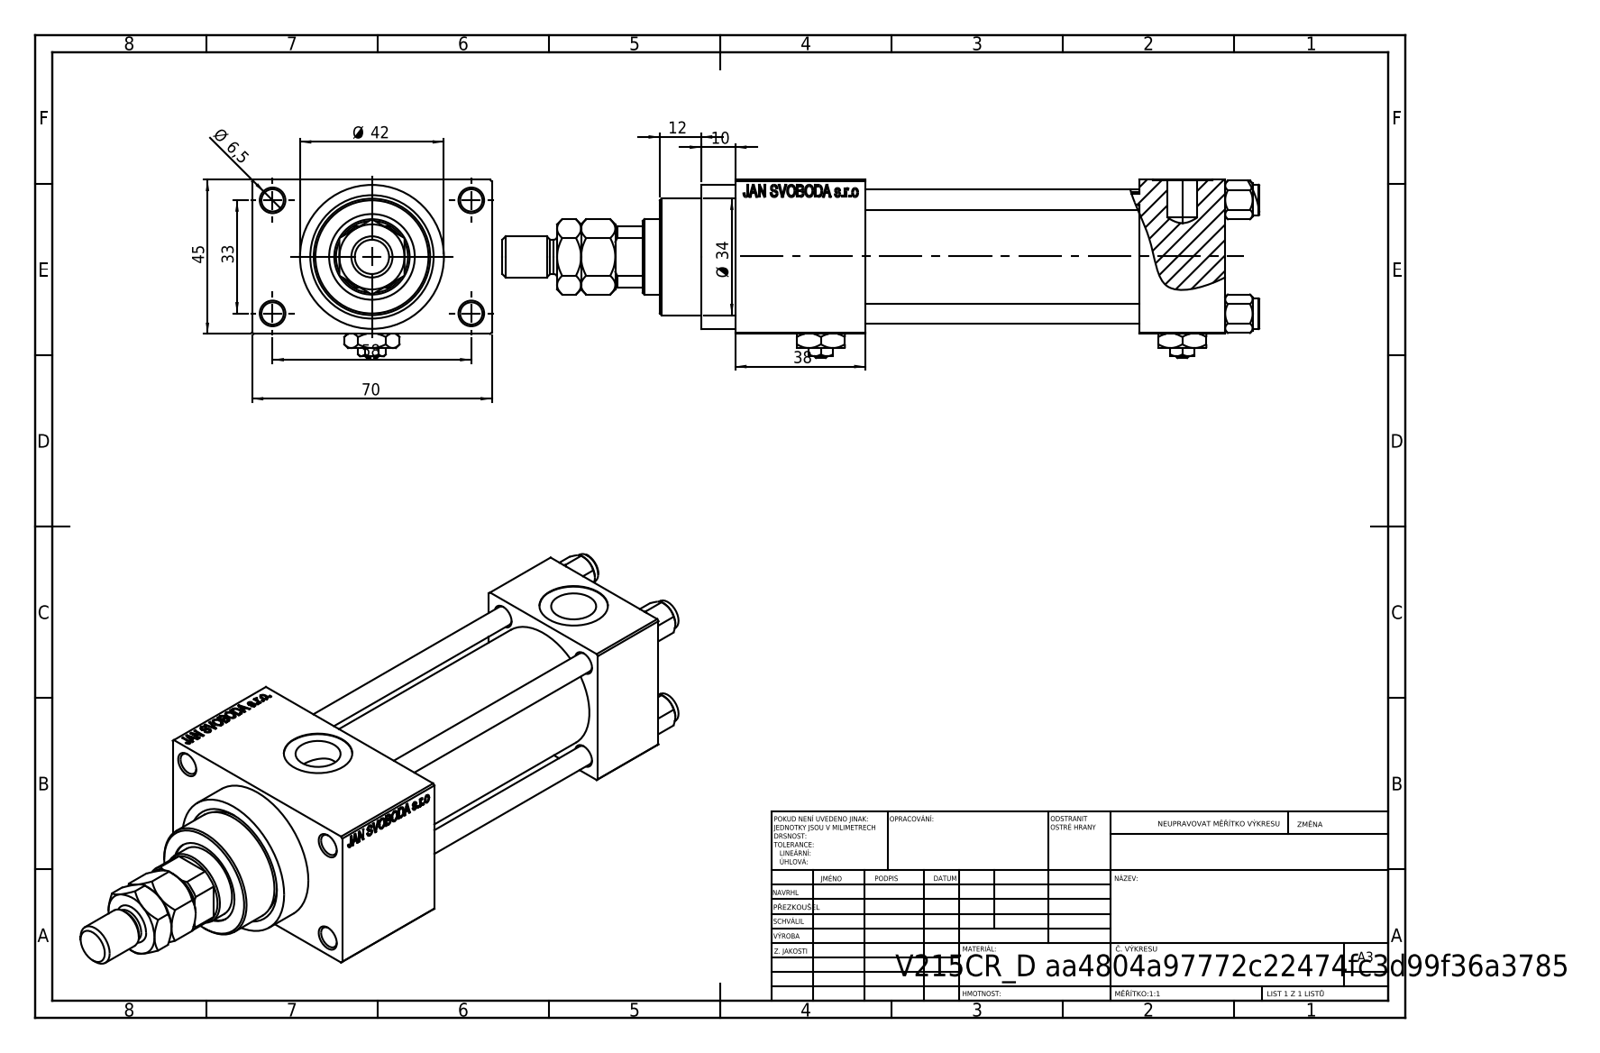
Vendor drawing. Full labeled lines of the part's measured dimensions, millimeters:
Part name (STEP PRODUCT): V215CR_D_TYCINKA; MTA; NUT_M5_D; V215_VC_A (+3 more)
STEP written by: SolidWorks 2019 (CONFIG_CONTROL_DESIGN)
Units: millimetres
Bodies: 14 solids, 1253 faces (557 planar, 104 cylindrical, 592 other)
Overall size (bounding box): 221 × 70 × 52
Volume: 274 915 mm³ · Surface area: 94 363 mm²
Round holes (diameter × count): ⌀6 ×4, ⌀6.5 ×4, ⌀7 ×2, ⌀13.16 ×2, ⌀20 ×2, ⌀10.5 ×1, ⌀22 ×1, ⌀24 ×1, ⌀25 ×1, ⌀32 ×1, ⌀33 ×1
Round bosses / shafts (diameter × count): ⌀9 ×4, ⌀42 ×1, ⌀38 ×1, ⌀34 ×1, ⌀12 ×1, ⌀10 ×1
Partial cylindrical surfaces — rounded edges, fillets, slot ends (radius × count): R10.5 ×1
Main face-to-face distances: 45, 25, 12.5, 57.5, 80, 105, 118, 70, 38, 143
Hole centre spacings: 12.4, 23.48, 33.2, 33.37, 35.35, 45.6, 56.35, 33
